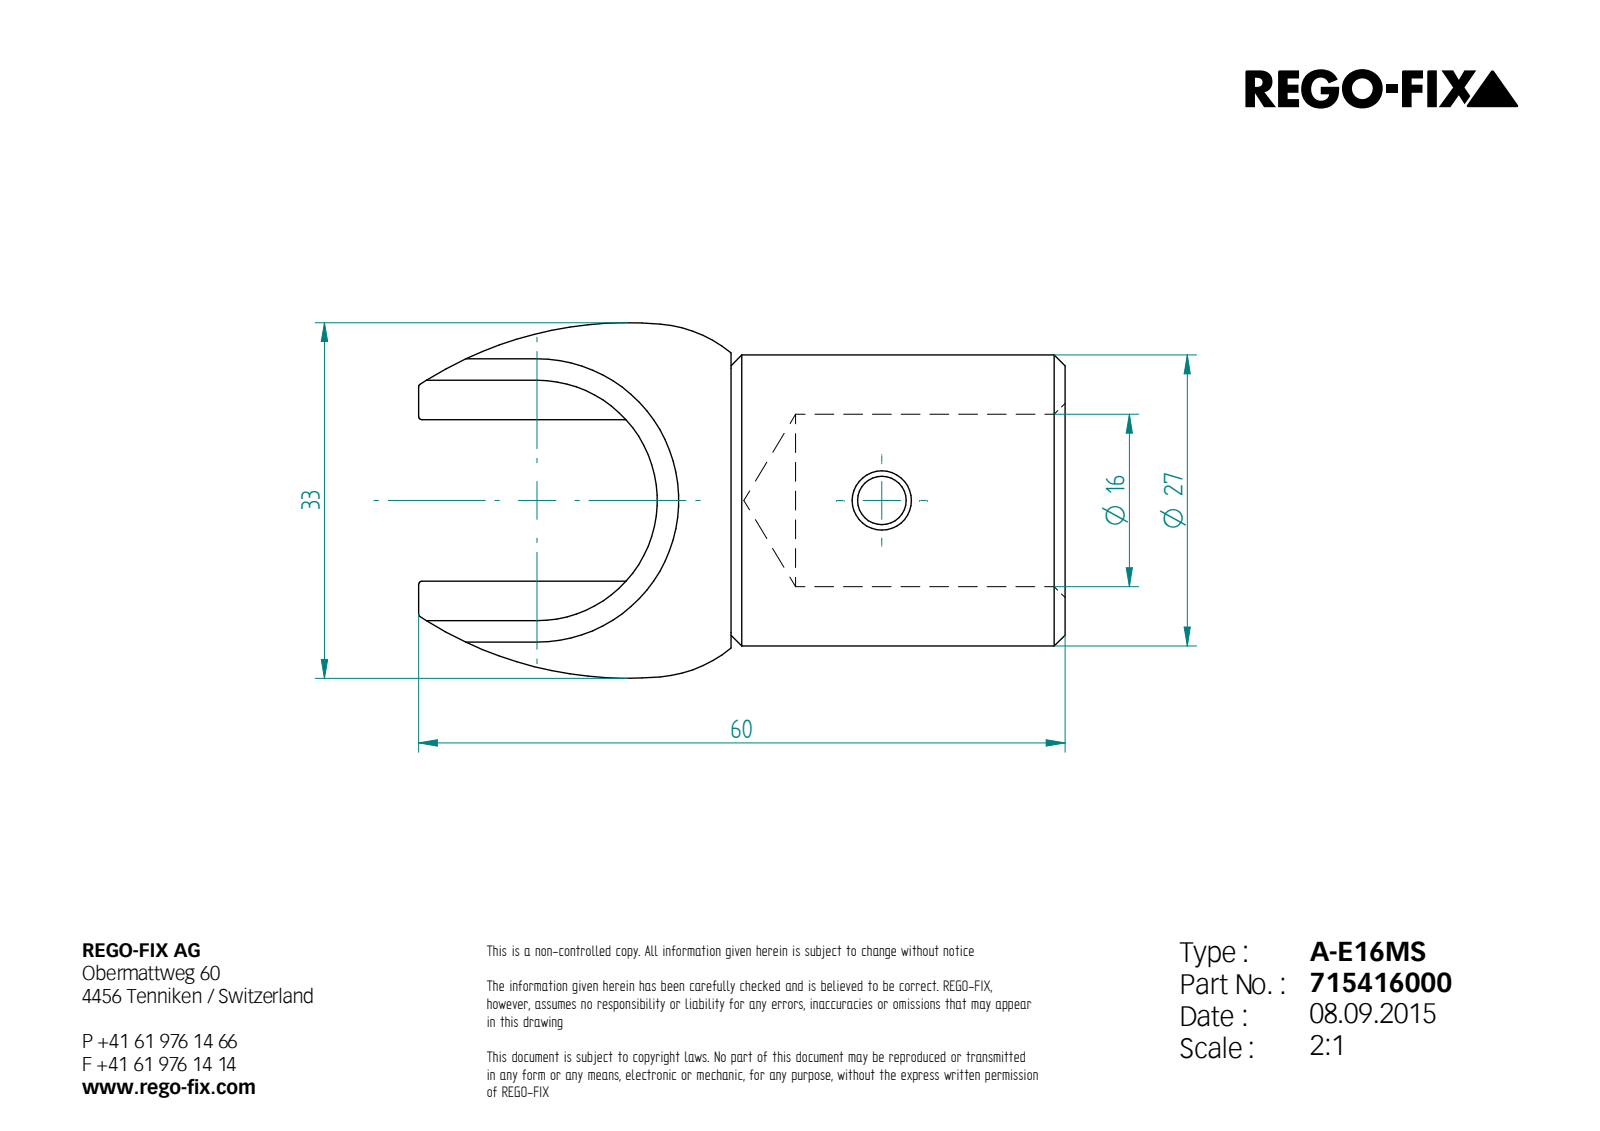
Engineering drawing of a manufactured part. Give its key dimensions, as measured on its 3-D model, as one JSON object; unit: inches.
{"step_written_by": "Unknown (AUTOMOTIVE_DESIGN)", "units": "inches", "bodies": {"solids": 1, "faces": 40, "planar": 19, "cylindrical": 14, "other": 7}, "overall_size": [2.362, 1.299, 1.063], "volume_in3": 0.86, "surface_area_in2": 10.03, "round_holes": [[0.177, 1], [0.217, 1], [0.63, 1]], "round_bosses_or_shafts": [[1.063, 1]], "partial_cylinders_radius": [[0.012, 4], [0.472, 2], [1.39, 2], [0.439, 1]], "face_to_face_distances": [0.197, 0.079, 0.118, 1.22, 0.039, 0.593, 0.591, 1.142, 2.362]}
